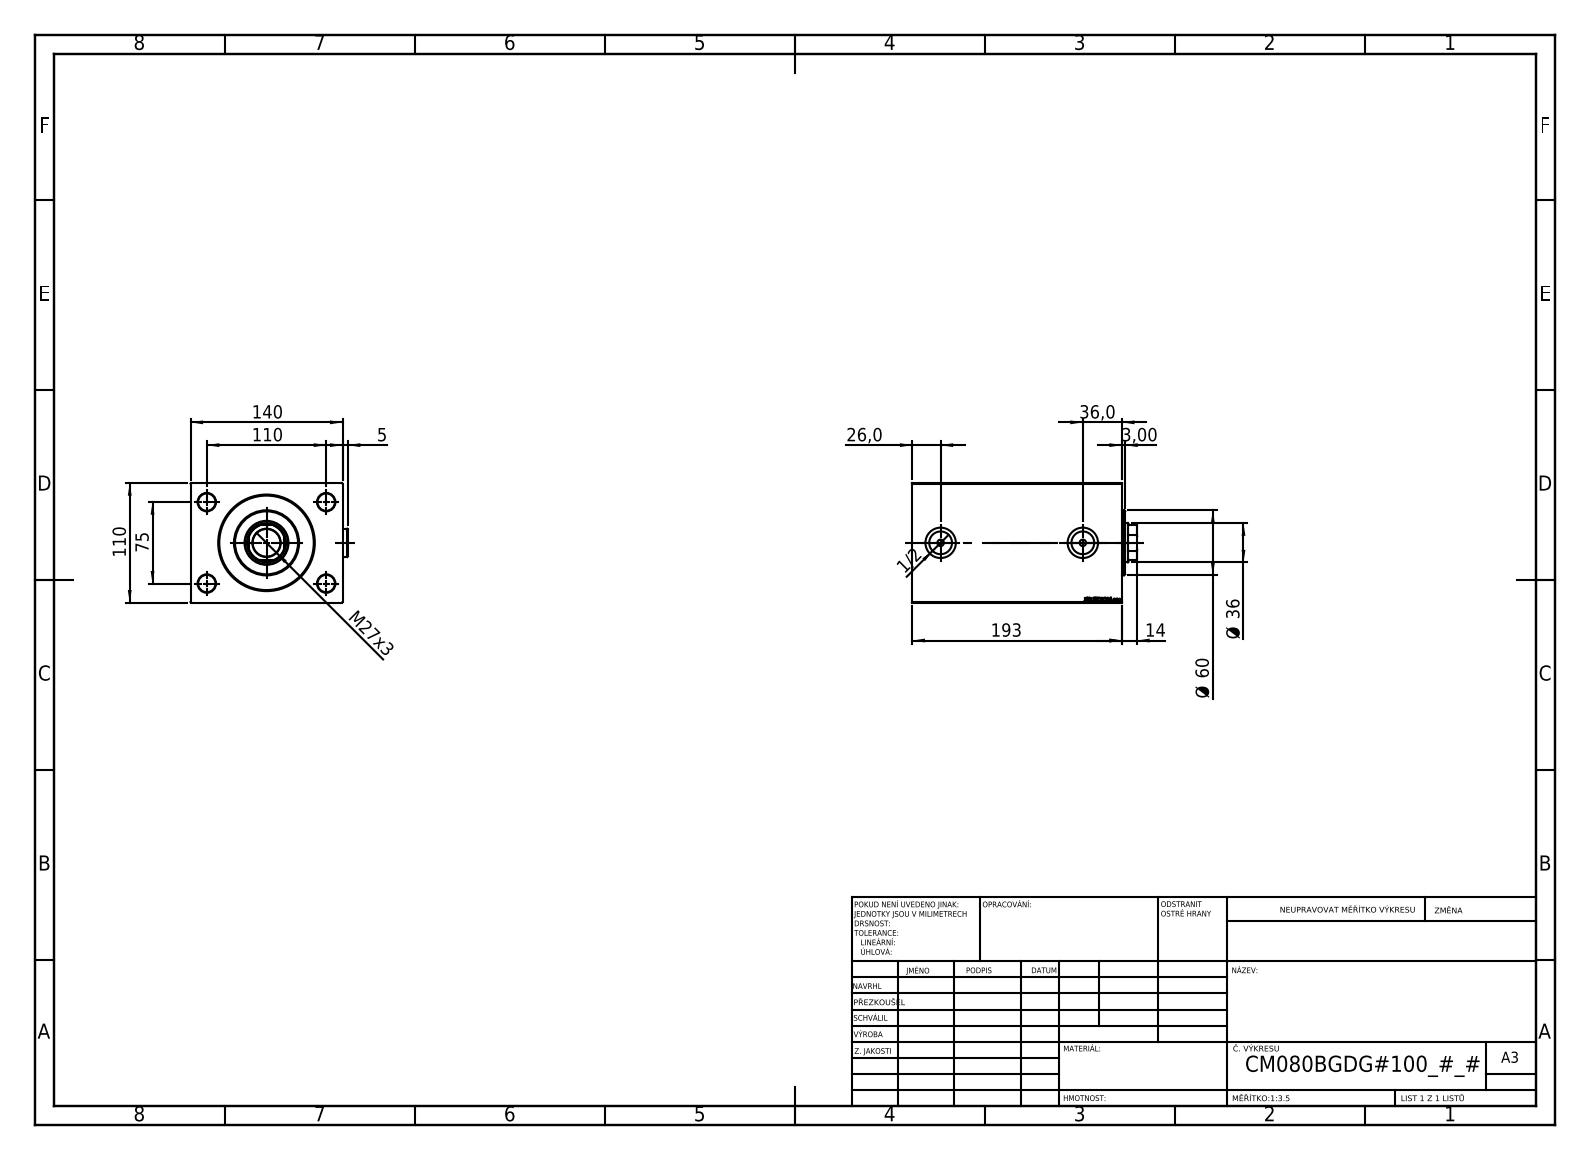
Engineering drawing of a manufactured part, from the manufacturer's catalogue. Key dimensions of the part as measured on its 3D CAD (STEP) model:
Part name (STEP PRODUCT): V450CM_B_VCP; V450CM_VC_B; Zatka_OIL_PORT; V450CM_B_Body
STEP written by: SolidWorks 2019 (CONFIG_CONTROL_DESIGN)
Units: millimetres
Bodies: 5 solids, 938 faces (436 planar, 72 cylindrical, 430 other)
Overall size (bounding box): 207 × 144.9 × 110
Volume: 2 506 000 mm³ · Surface area: 247 842 mm²
Round holes (diameter × count): ⌀16 ×4, ⌀6 ×2, ⌀20.96 ×2, ⌀28 ×2, ⌀25.5 ×1, ⌀36 ×1, ⌀39.5 ×1, ⌀40.5 ×1, ⌀80 ×1, ⌀82 ×1, ⌀87 ×1
Round bosses / shafts (diameter × count): ⌀26 ×2, ⌀60 ×1
Partial cylindrical surfaces — rounded edges, fillets, slot ends (radius × count): R17.5 ×1
Main face-to-face distances: 110, 140, 193, 172, 21, 14, 158, 179, 114, 100
Hole centre spacings: 66.57, 75, 110, 133.14, 131
